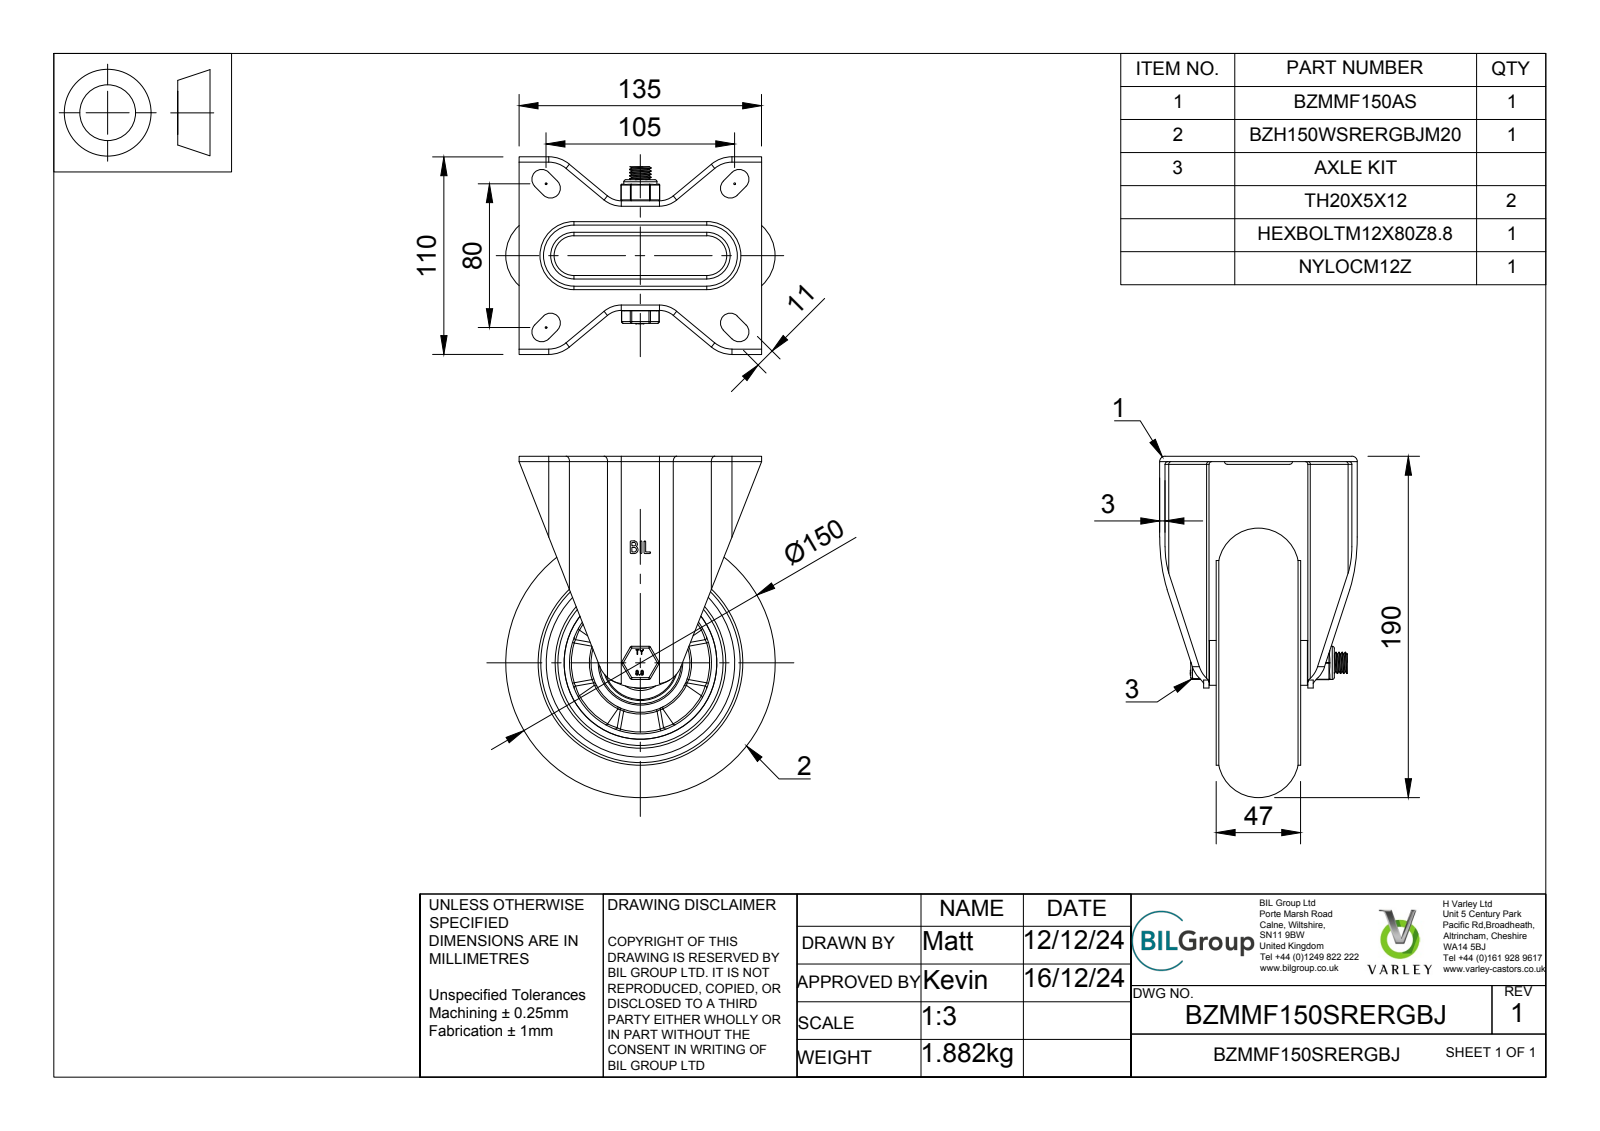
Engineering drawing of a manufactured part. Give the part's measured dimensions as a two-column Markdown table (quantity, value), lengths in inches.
| quantity | value |
| --- | --- |
| part name | BZMMF150SRERGBJ v3; BZMMF150AS - 55 v1; ZINC PLATED, PRESSED STEEL BRACKET; BZH150WSRERGBJM20 v1 (+7 more) |
| STEP written by | Autodesk Translation Framework v13.20.0.188 (AP242_MANAGED_MODEL_BASED_3D_ENGINEERING_MIM_LF) |
| units | inches |
| bodies | 35 solids, 1258 faces (438 planar, 238 cylindrical, 582 other) |
| overall size | 7.48 × 5.906 × 4.331 |
| volume | 41.02 in³ |
| surface area | 336.1 in² |
| round holes (diameter × count) | 0.472 × 1, 0.482 × 1, 0.492 × 1, 0.551 × 1, 0.787 × 1, 1.122 × 1, 1.213 × 1, 1.587 × 1, 1.594 × 1, 1.654 × 1, 1.693 × 1, 1.85 × 1 |
| round bosses / shafts (diameter × count) | 4.488 × 1, 3.74 × 1, 2.165 × 1, 1.606 × 1, 1.232 × 1, 1.063 × 1, 0.984 × 1, 0.906 × 1 |
| partial cylindrical surfaces (radius × count) | 0.02 × 18, 0.039 × 12, 0.059 × 12, 0.118 × 8, 0.217 × 8, 0.079 × 4, 0.236 × 4, 0.354 × 4 |
| main face-to-face distances | 0.118, 0.974, 0.856, 0.315, 1.092, 2.283, 0.433, 0.197, 1.969, 1.535 |
